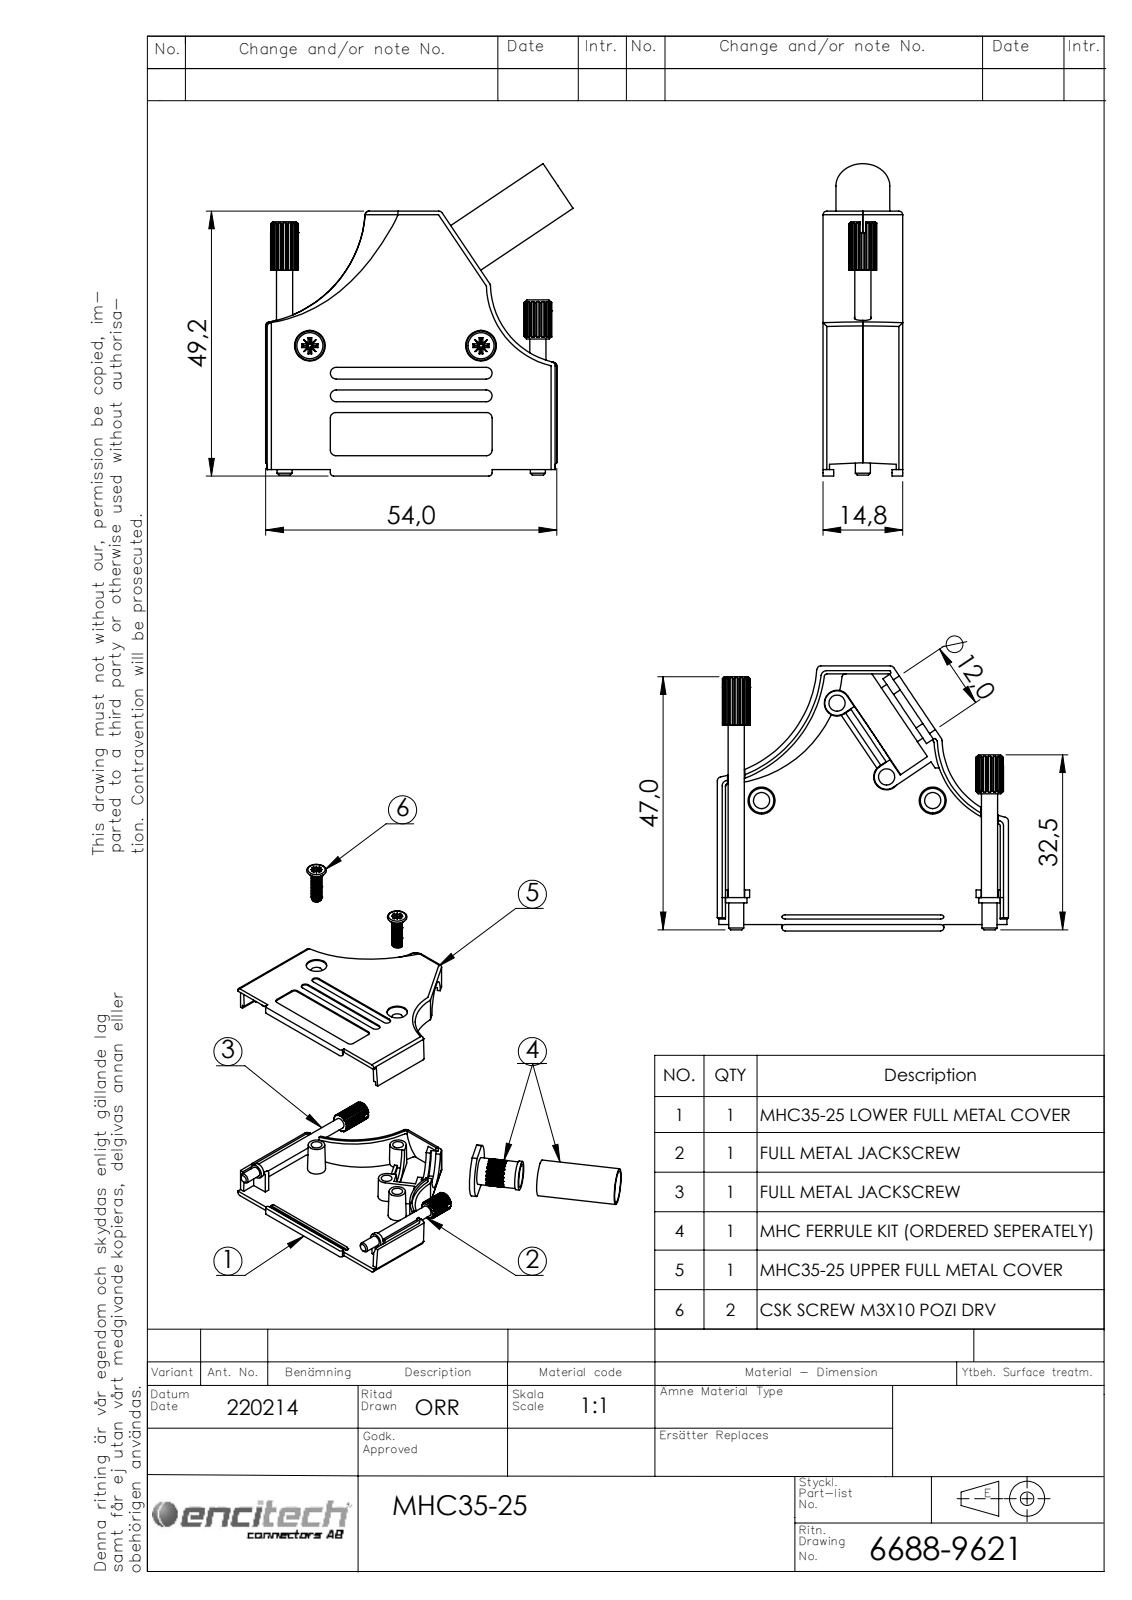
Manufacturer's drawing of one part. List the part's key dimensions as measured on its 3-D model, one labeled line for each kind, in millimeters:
Part name (STEP PRODUCT): 6826-0141-01; 6805-0139-03; 6560-0138-13; 6522-0110-12 (+4 more)
STEP written by: SolidWorks 2021 (AUTOMOTIVE_DESIGN)
Units: millimetres
Bodies: 8 solids, 1683 faces (373 planar, 421 cylindrical, 889 other)
Overall size (bounding box): 58.01 × 57.03 × 14.8
Volume: 9 010 mm³ · Surface area: 16 332 mm²
Round holes (diameter × count): ⌀3 ×4, ⌀3.2 ×2, ⌀4.8 ×2, ⌀5.7 ×2, ⌀6.5 ×1, ⌀8.8 ×1, ⌀12 ×1
Round bosses / shafts (diameter × count): ⌀4 ×2, ⌀3 ×2, ⌀2.9 ×2, ⌀2.8 ×2, ⌀10 ×1, ⌀8 ×1, ⌀7.5 ×1
Partial cylindrical surfaces — rounded edges, fillets, slot ends (radius × count): R0.75 ×10, R0.1 ×8, R1 ×7, R1.1 ×4, R0.3 ×3, R0.38 ×3, R0.5 ×3, R0.6 ×2
Main face-to-face distances: 1.2, 13.6, 12.4, 14.8, 0.9, 14.5, 13.3, 6.2, 7.4, 7.1
Hole centre spacings: 9.61, 16.5, 22.87, 23.61, 25.34, 31.75, 47
